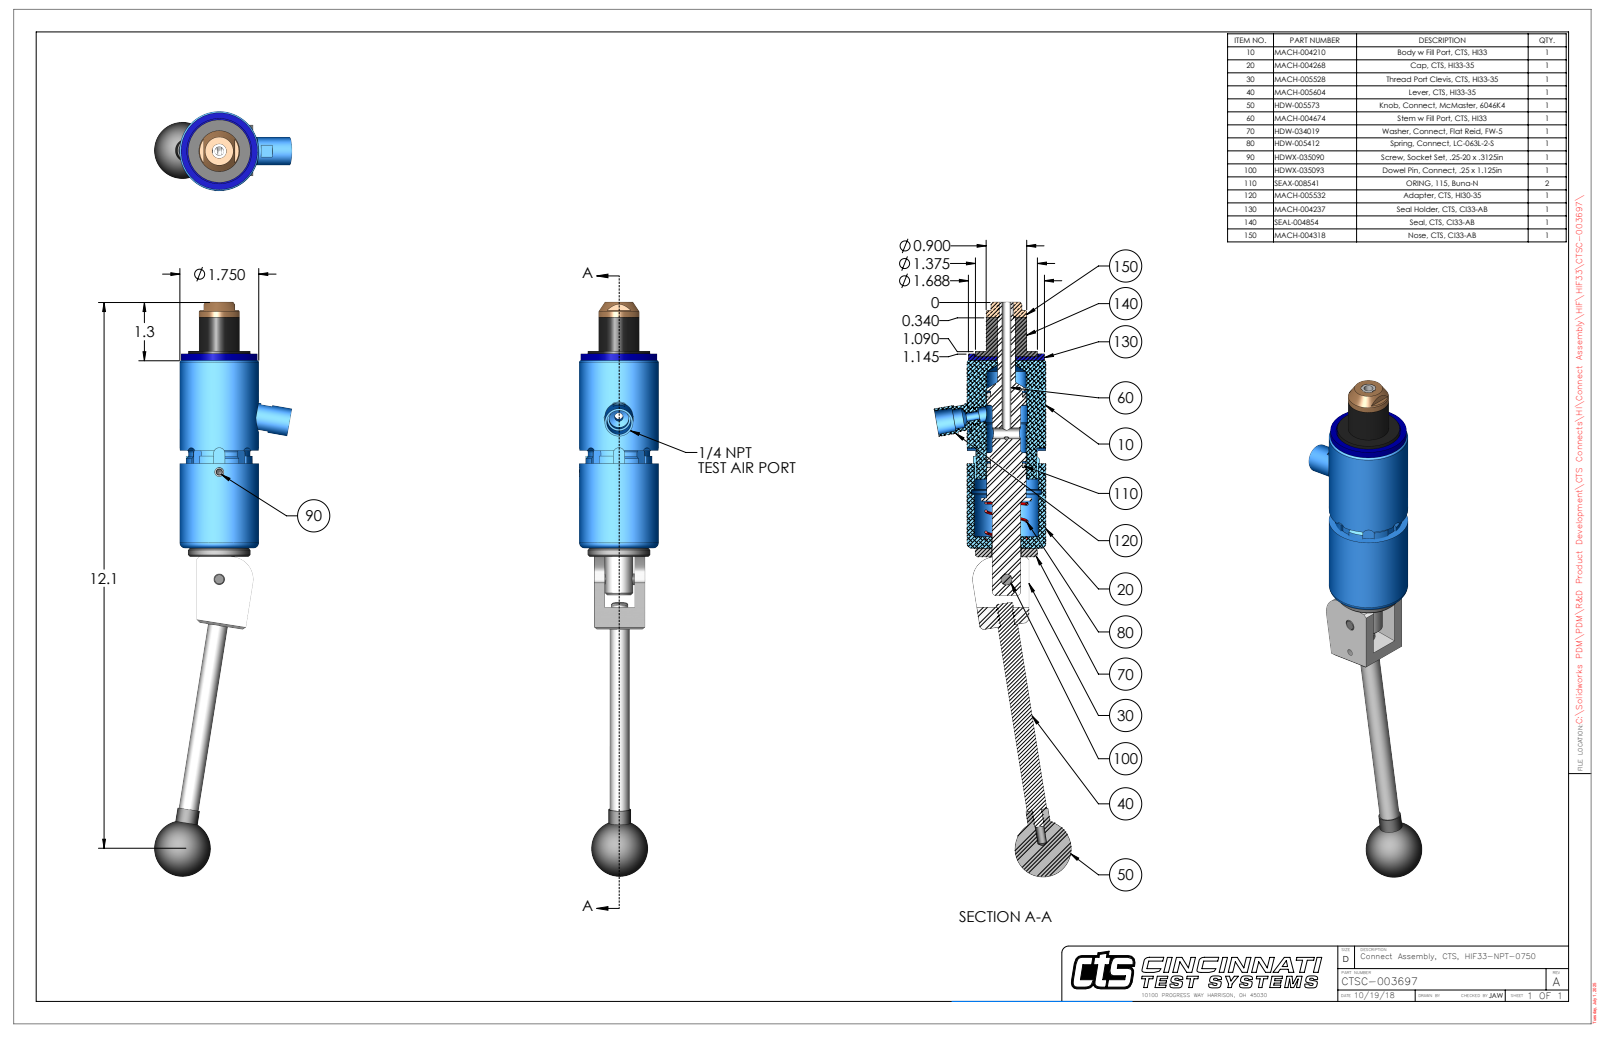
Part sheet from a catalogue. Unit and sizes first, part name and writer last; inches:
Units: inches
Overall size (bounding box): 12.729 × 3.043 × 1.75
Round holes (diameter × count): ⌀0.201 ×2, ⌀0.313 ×2, ⌀0.15 ×1, ⌀0.187 ×1, ⌀0.204 ×1, ⌀0.249 ×1, ⌀0.25 ×1, ⌀0.251 ×1, ⌀0.39 ×1, ⌀0.397 ×1, ⌀0.403 ×1, ⌀0.438 ×1
Round bosses / shafts (diameter × count): ⌀0.312 ×2, ⌀0.25 ×2, ⌀1.75 ×1, ⌀1.687 ×1, ⌀1.38 ×1, ⌀1.375 ×1, ⌀0.9 ×1, ⌀0.625 ×1
Partial cylindrical surfaces — rounded edges, fillets, slot ends (radius × count): R0.125 ×4, R0.029 ×2, R0.153 ×1, R0.33 ×1, R0.5 ×1, R0.695 ×1, R0.709 ×1, R0.744 ×1
Main face-to-face distances: 0.082, 4.244, 4.162, 1.12, 4.432, 4.35, 0.188, 0.888, 0.232, 0.232
Hole centre spacings: 0.74, 2.376, 3.116
Volume: 14.14 in³ · Surface area: 80.11 in²
Bodies: 9 solids, 309 faces (114 planar, 134 cylindrical, 61 other)
Part name (STEP PRODUCT): CTSC-003697
STEP written by: SolidWorks 2023 (AUTOMOTIVE_DESIGN)
